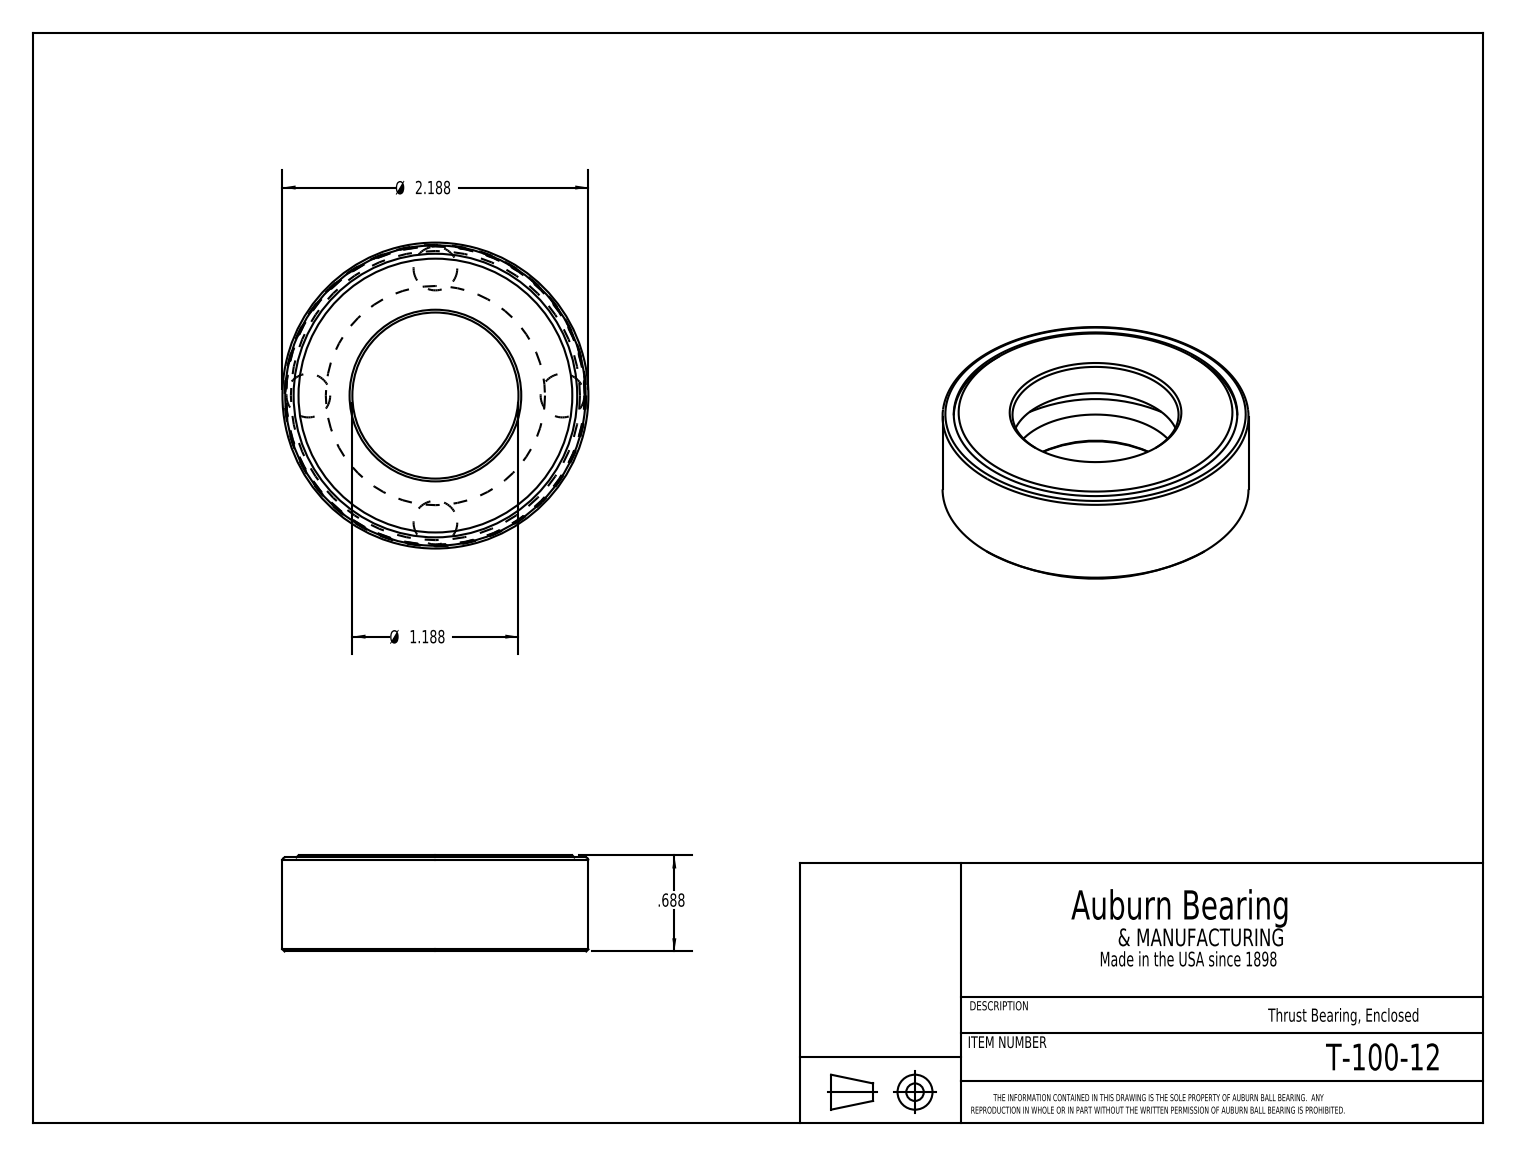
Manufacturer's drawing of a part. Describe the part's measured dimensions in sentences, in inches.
The part is named "T-100-12". Its 3-D file was written by "SolidWorks 2016 (CONFIG_CONTROL_DESIGN)". It is 6 solids with 28 faces: 9 planar, 7 cylindrical and 12 other. Overall it measures 2.188 by 2.188 by 0.688 inches. Its volume is 1.256 cubic inches and its surface area 23.2 square inches. Round holes: 1 of diameter 1.187, 1 of diameter 2.027, 1 of diameter 2.147. Round bosses or shafts: 1 of diameter 2.187, 1 of diameter 2.133. The main face-to-face distances are 0.25, 0.437, 0.687, 0.187, 0.672, 0.422, 0.235, 0.015, 0.652, 0.402.
